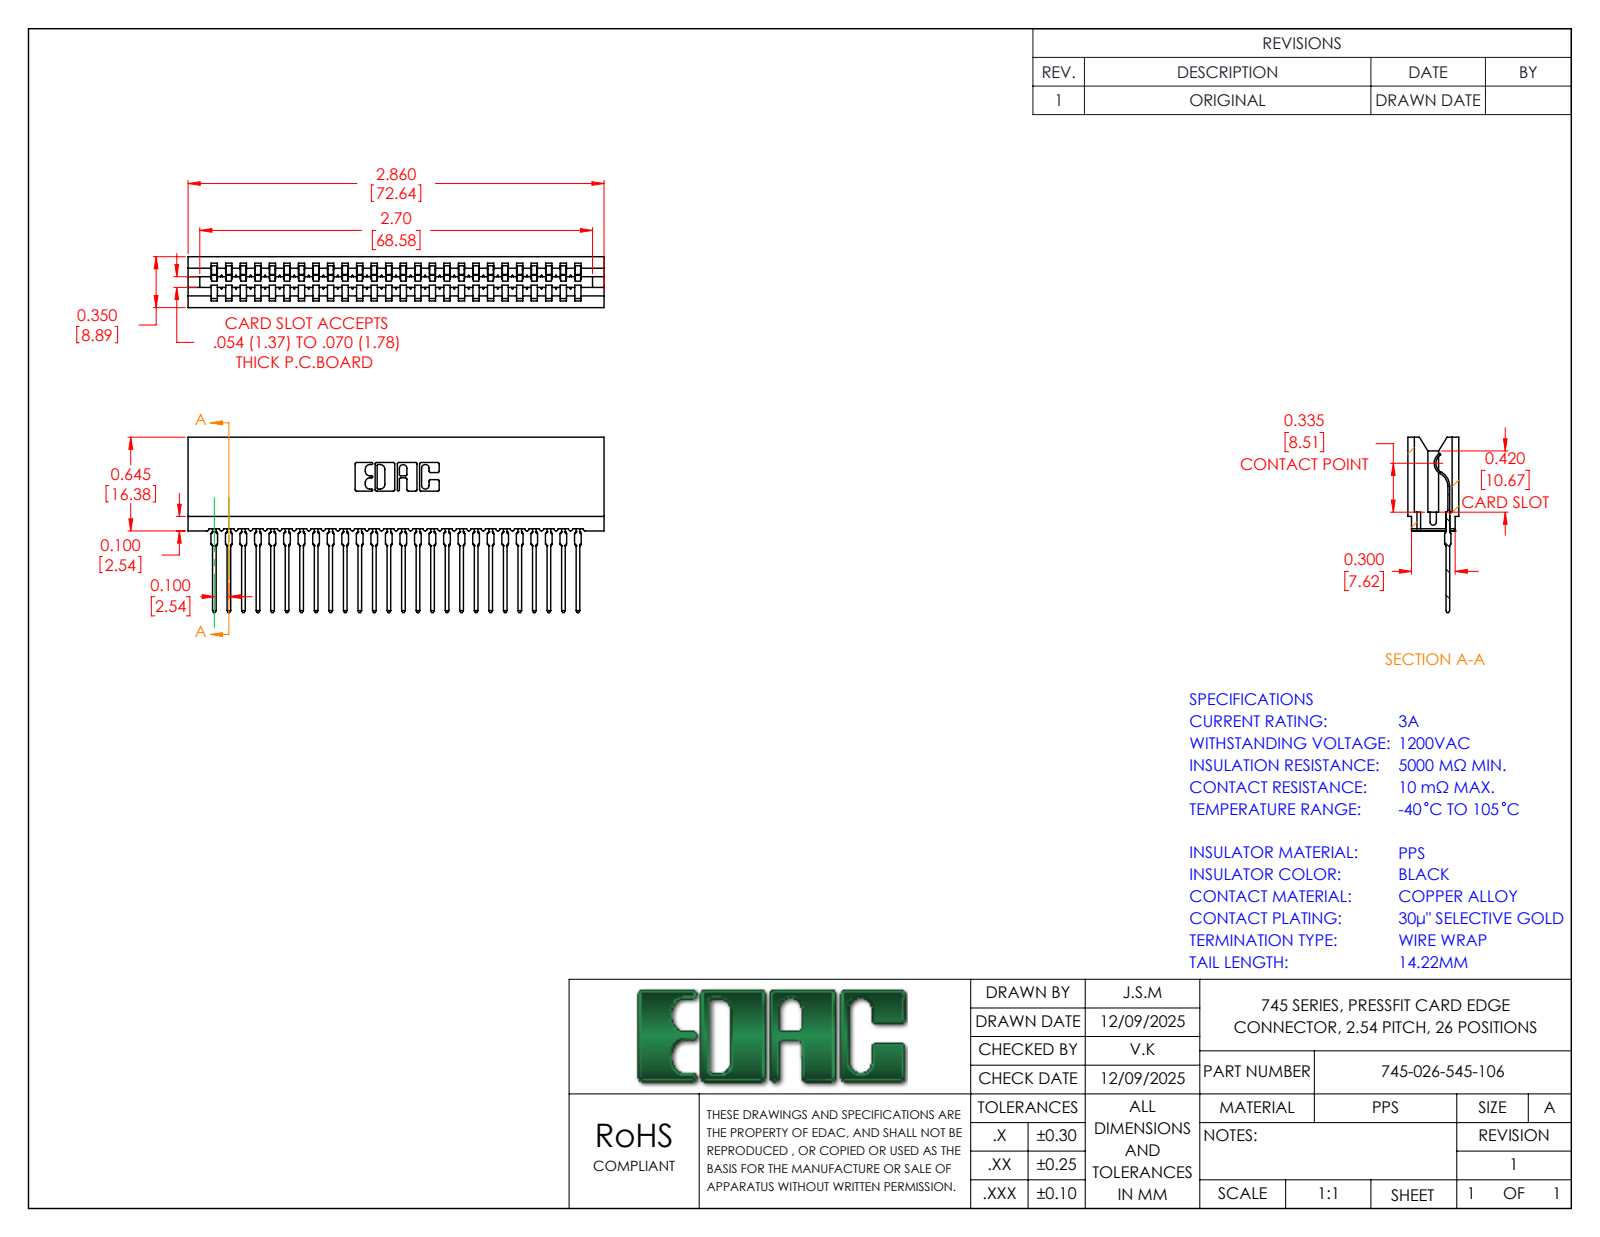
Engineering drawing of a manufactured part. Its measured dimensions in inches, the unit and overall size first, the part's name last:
Units: inches
Overall size (bounding box): 2.86 × 1.206 × 0.35
Partial cylindrical surfaces — rounded edges, fillets, slot ends (radius × count): R0.015 ×52, R0.022 ×52, R0.01 ×22, R0.007 ×6, R0.031 ×6, R0.005 ×4, R0.011 ×4, R0.026 ×3
Main face-to-face distances: 0.1, 0.2, 0.35, 0.3, 0.7, 0.6, 0.5, 0.4, 0.138, 0.212
Volume: 0.394 in³ · Surface area: 18.78 in²
Bodies: 27 solids, 3008 faces (1798 planar, 534 cylindrical, 676 other)
Part name (STEP PRODUCT): 745-292-001_545; 745 Part_Insulator Option - 06; 745-026-545-106
STEP written by: SolidWorks 2023 (CONFIG_CONTROL_DESIGN)
